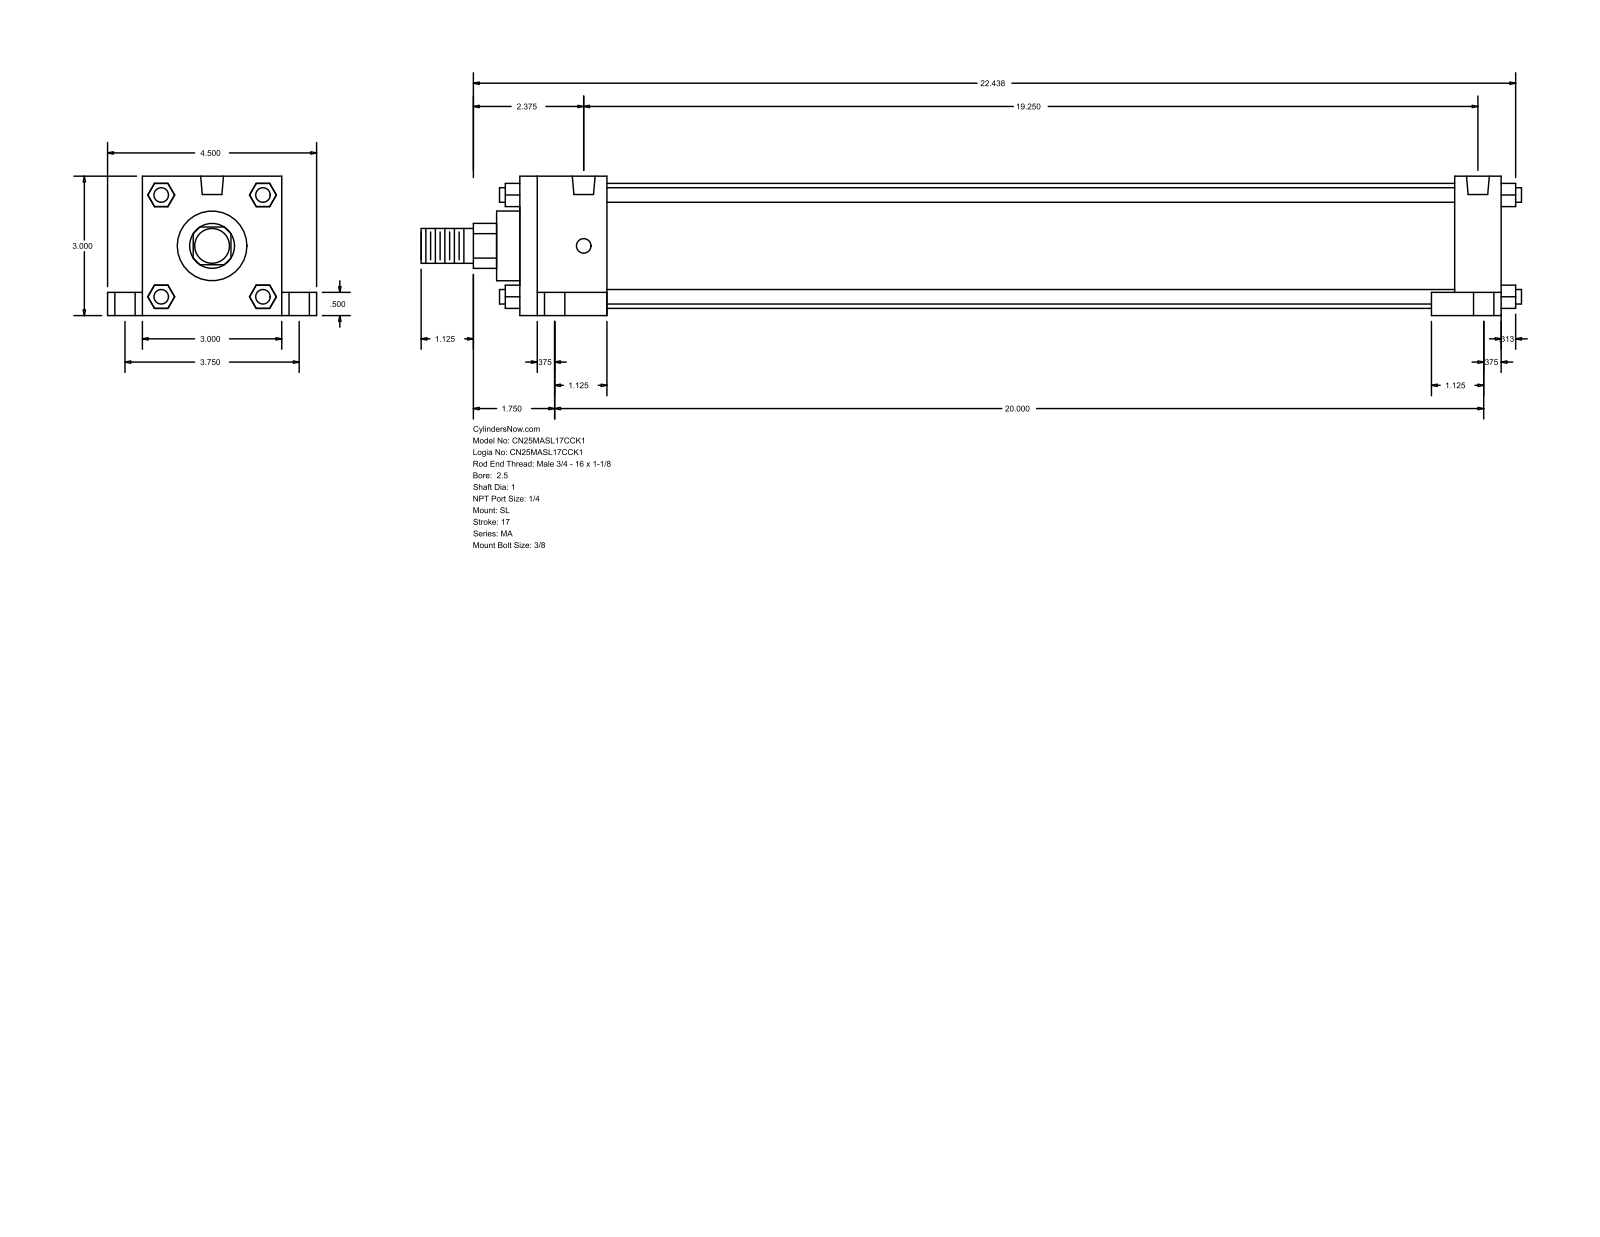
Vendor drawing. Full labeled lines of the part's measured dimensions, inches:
Part name (STEP PRODUCT): MA_SL__0250_1
STEP written by: GSSL Pune (CONFIG_CONTROL_DESIGN)
Units: inches
Bodies: 0 solids, 148 faces (112 planar, 36 cylindrical, 0 other)
Overall size (bounding box): 23.687 × 4.5 × 3
Round holes (diameter × count): ⌀0.313 ×4, ⌀0.437 ×4, ⌀0.687 ×4, ⌀0.492 ×2
Round bosses / shafts (diameter × count): ⌀0.313 ×4, ⌀2.69 ×1, ⌀1.5 ×1, ⌀1 ×1, ⌀0.75 ×1
Partial cylindrical surfaces — rounded edges, fillets, slot ends (radius × count): R0.484 ×1
Main face-to-face distances: 3, 21.125, 0.5, 18.25, 1, 1.875, 19.25, 20.125, 0.75, 3.75
Hole centre spacings: 1.879, 1.976, 3.75, 19.25, 19.465, 19.963, 20, 20.348
